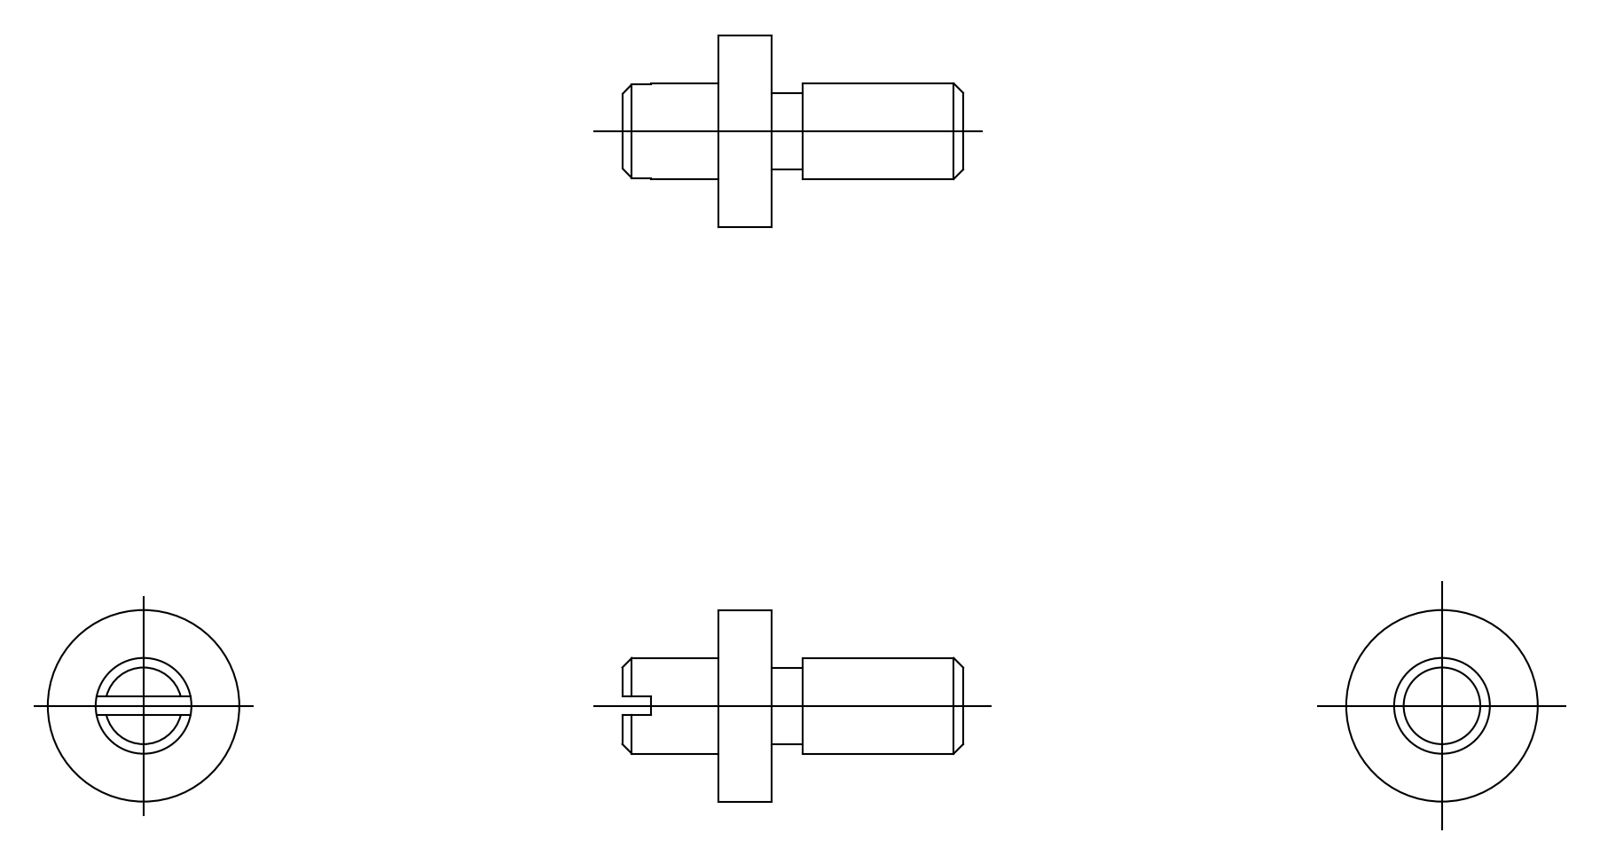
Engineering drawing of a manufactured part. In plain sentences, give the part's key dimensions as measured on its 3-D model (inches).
Its 3-D file was written by "spGate 19.8.4 (****-****-****-****) (AUTOMOTIVE_DESIGN)". It is 1 solid with 21 faces: 9 planar, 8 cylindrical and 4 other. Overall it measures 0.701 by 0.394 by 0.394 inches. Its volume is 0.03 cubic inches and its surface area 0.763 square inches. Round bosses or shafts: 1 of diameter 0.394, 1 of diameter 0.197, 1 of diameter 0.157. The main face-to-face distances are 0.11, 0.504, 0.394, 0.197, 0.307, 0.701, 0.039, 0.37, 0.173, 0.063.
